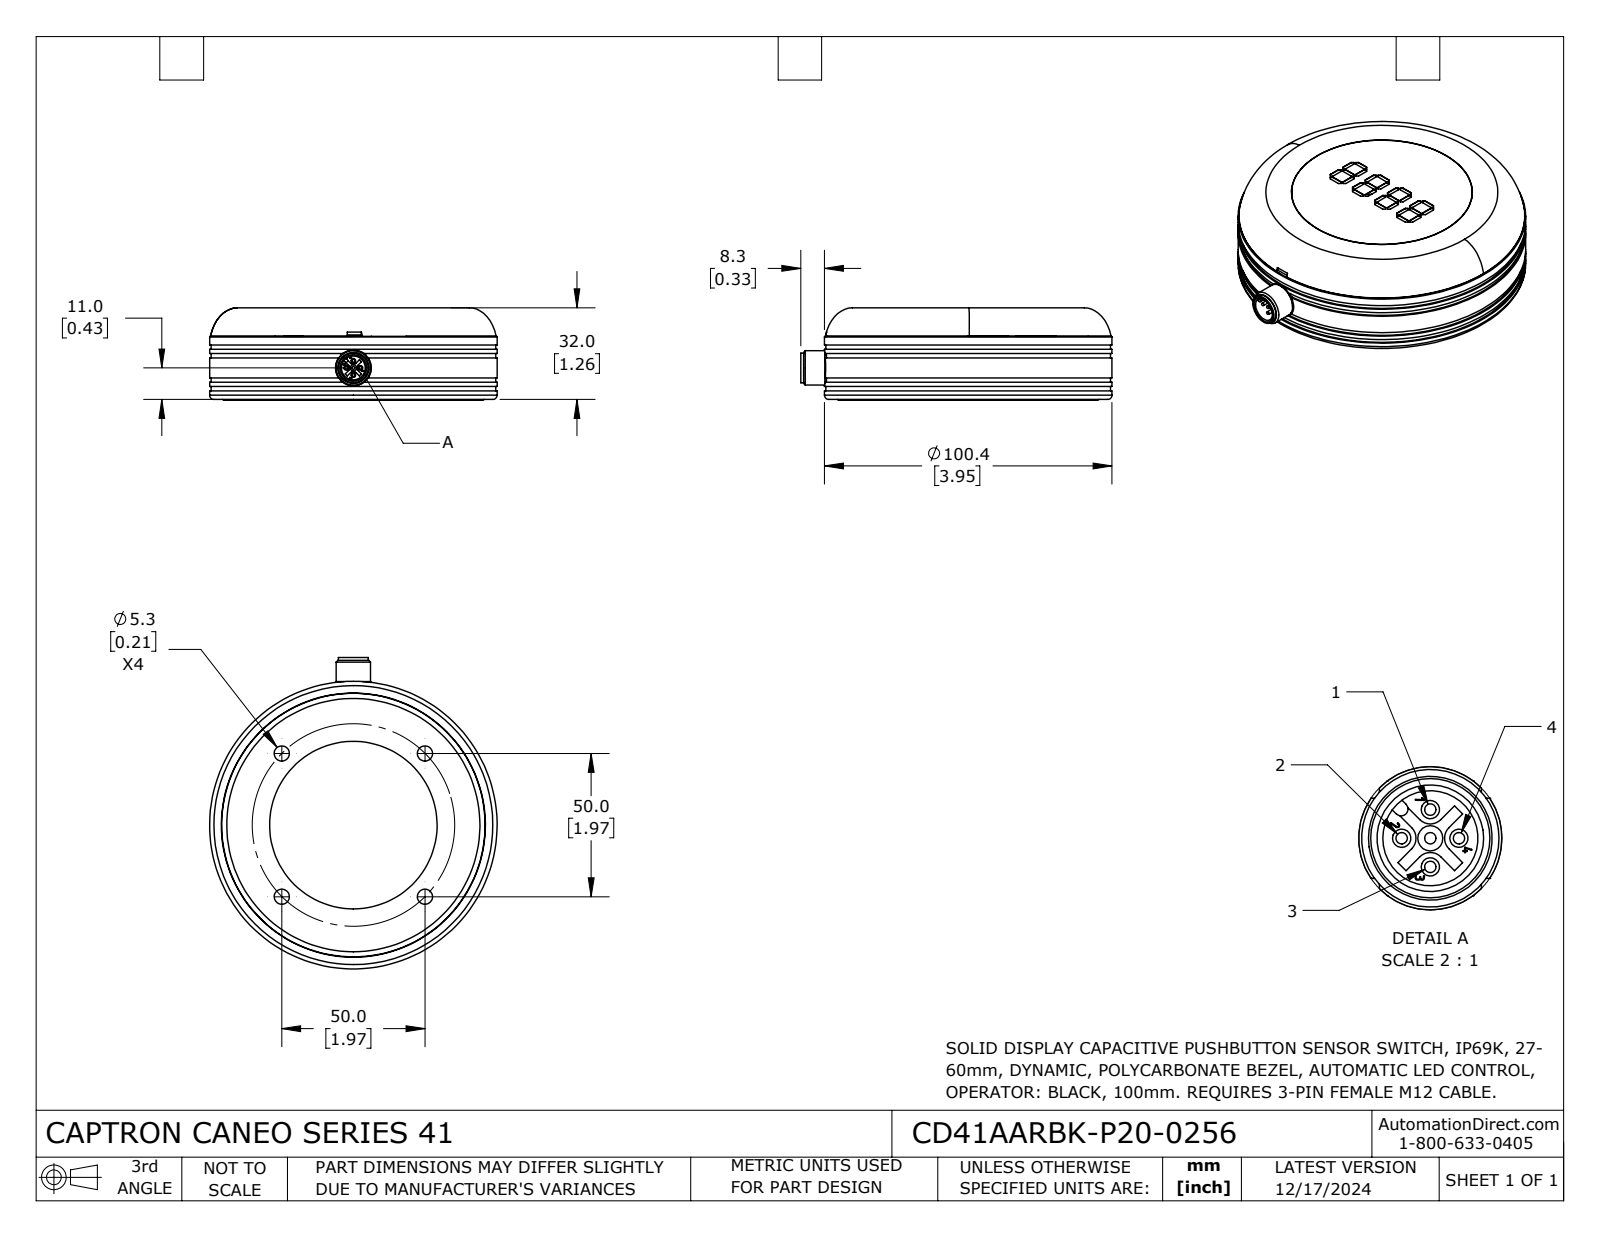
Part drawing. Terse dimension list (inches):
name: CD41AARBK-P20-0256
written by: SolidWorks 2024 (CONFIG_CONTROL_DESIGN)
unit: in
bodies: 1 solid, 386 faces (254 planar, 73 cylindrical, 59 other)
size: 4.28 × 3.953 × 1.272
volume: 14.85 in³; area: 44.38 in²
holes: 4× ⌀0.209, 1× ⌀0.327, 1× ⌀0.374, 1× ⌀0.492, 1× ⌀2.303, 1× ⌀3.63
bosses: 5× ⌀0.039, 1× ⌀3.953, 1× ⌀3.913, 1× ⌀3.48, 1× ⌀2.48, 1× ⌀0.472, 1× ⌀0.409, 1× ⌀0.37
rounds: 4× R0.051, 1× R0.024, 1× R1.969
face distances: 1.26, 1.252, 1.26, 1.252, 0.059, 0.118, 0.571, 0.512, 0.453, 0.63
hole spacings: 1.392, 1.969, 2.784
